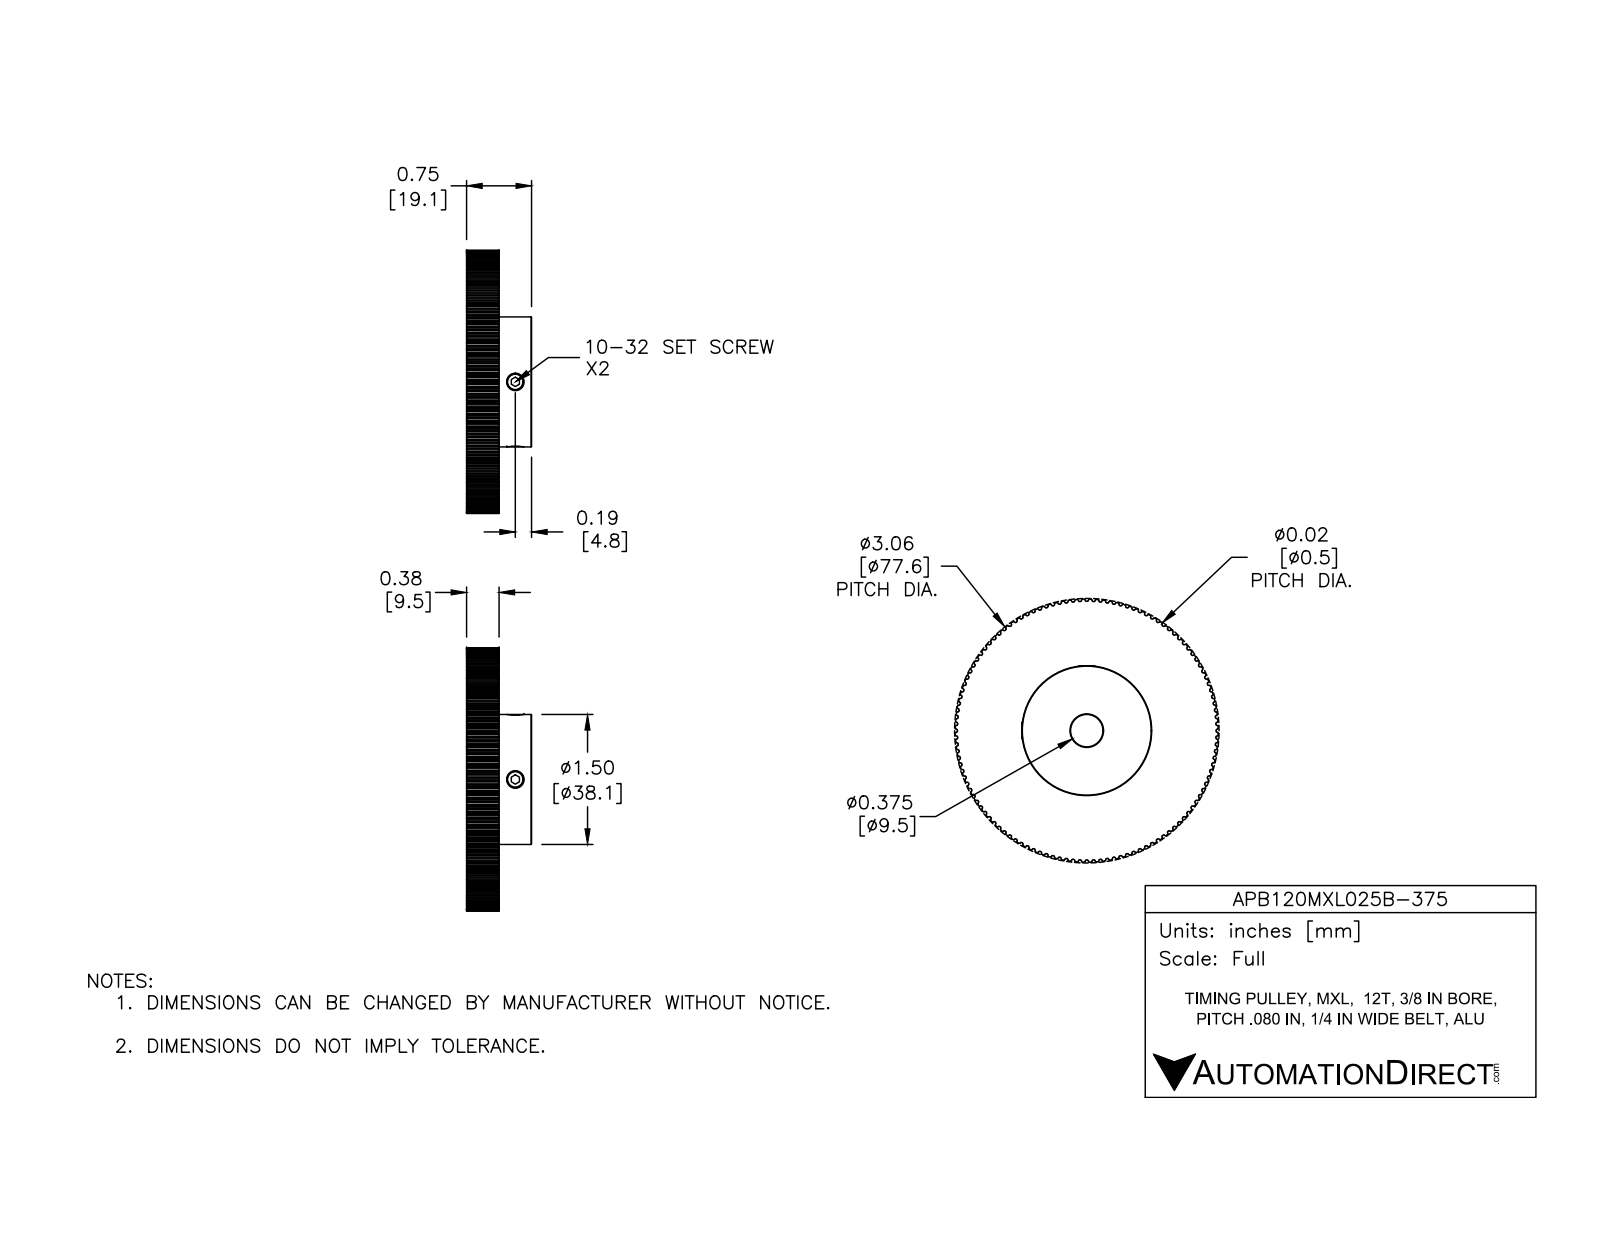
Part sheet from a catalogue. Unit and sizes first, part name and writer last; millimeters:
Units: millimetres
Overall size (bounding box): 77.1 × 77.1 × 19.1
Round holes (diameter × count): ⌀4.8 ×2, ⌀9.5 ×1
Round bosses / shafts (diameter × count): ⌀4.8 ×2, ⌀38.1 ×1
Partial cylindrical surfaces — rounded edges, fillets, slot ends (radius × count): R0.2 ×240, R0.3 ×240, R38.6 ×1
Main face-to-face distances: 9.5, 19.1, 9.5, 25.3, 25.3, 25.3, 25.2, 75.8, 75.9, 75.9
Volume: 53 030 mm³ · Surface area: 14 490 mm²
Bodies: 3 solids, 1101 faces (381 planar, 706 cylindrical, 14 other)
Part name (STEP PRODUCT): APB120MXL025B-375
STEP written by: SolidWorks 2016 (AUTOMOTIVE_DESIGN)
